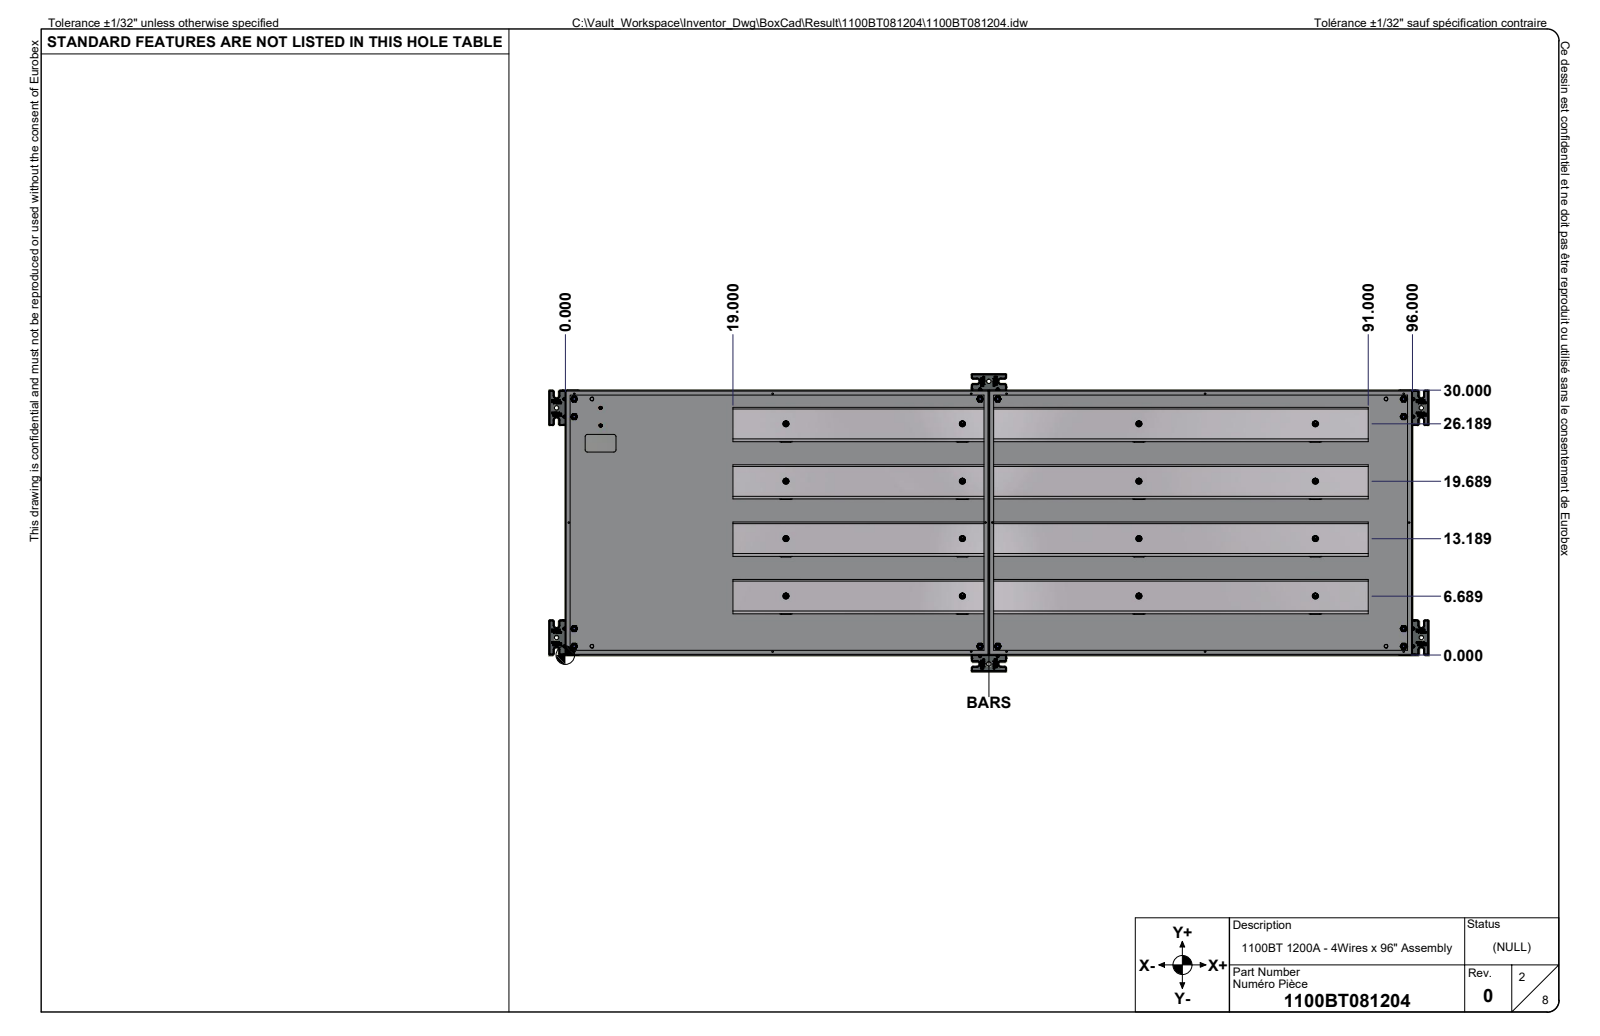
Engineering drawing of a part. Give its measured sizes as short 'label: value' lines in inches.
name: 1100BT081204; 1100BT081204B; 1100BT081204B-P; 1100BT081204E-P (+8 more)
written by: Autodesk Inventor 2024 (AUTOMOTIVE_DESIGN)
unit: in
bodies: 228 solids, 33252 faces (13704 planar, 9082 cylindrical, 10466 other)
size: 99.75 × 33.75 × 8.987
volume: 1 196 in³; area: 19 963 in²
holes: 64× ⌀0.177, 32× ⌀0.453, 22× ⌀0.315, 16× ⌀0.166, 16× ⌀0.262, 16× ⌀0.27, 16× ⌀0.562, 16× ⌀0.571, 12× ⌀0.339, 12× ⌀0.41, 12× ⌀0.551, 10× ⌀0.197
bosses: 26× ⌀0.374, 16× ⌀0.472, 16× ⌀0.307, 12× ⌀0.65, 12× ⌀0.382, 10× ⌀0.232, 4× ⌀0.571, 4× ⌀0.41
rounds: 464× R0.02, 464× R0.031, 210× R0.039, 192× R0.004, 140× R0.031, 138× R0.136, 116× R0.047, 116× R0.059
face distances: 0.068, 8, 7.932, 8.068, 1.657, 29.932, 3.315, 0.5, 30, 2.157
hole spacings: 0.61, 20, 6.315, 20.965, 6.285, 6.315, 19.39, 20.383
